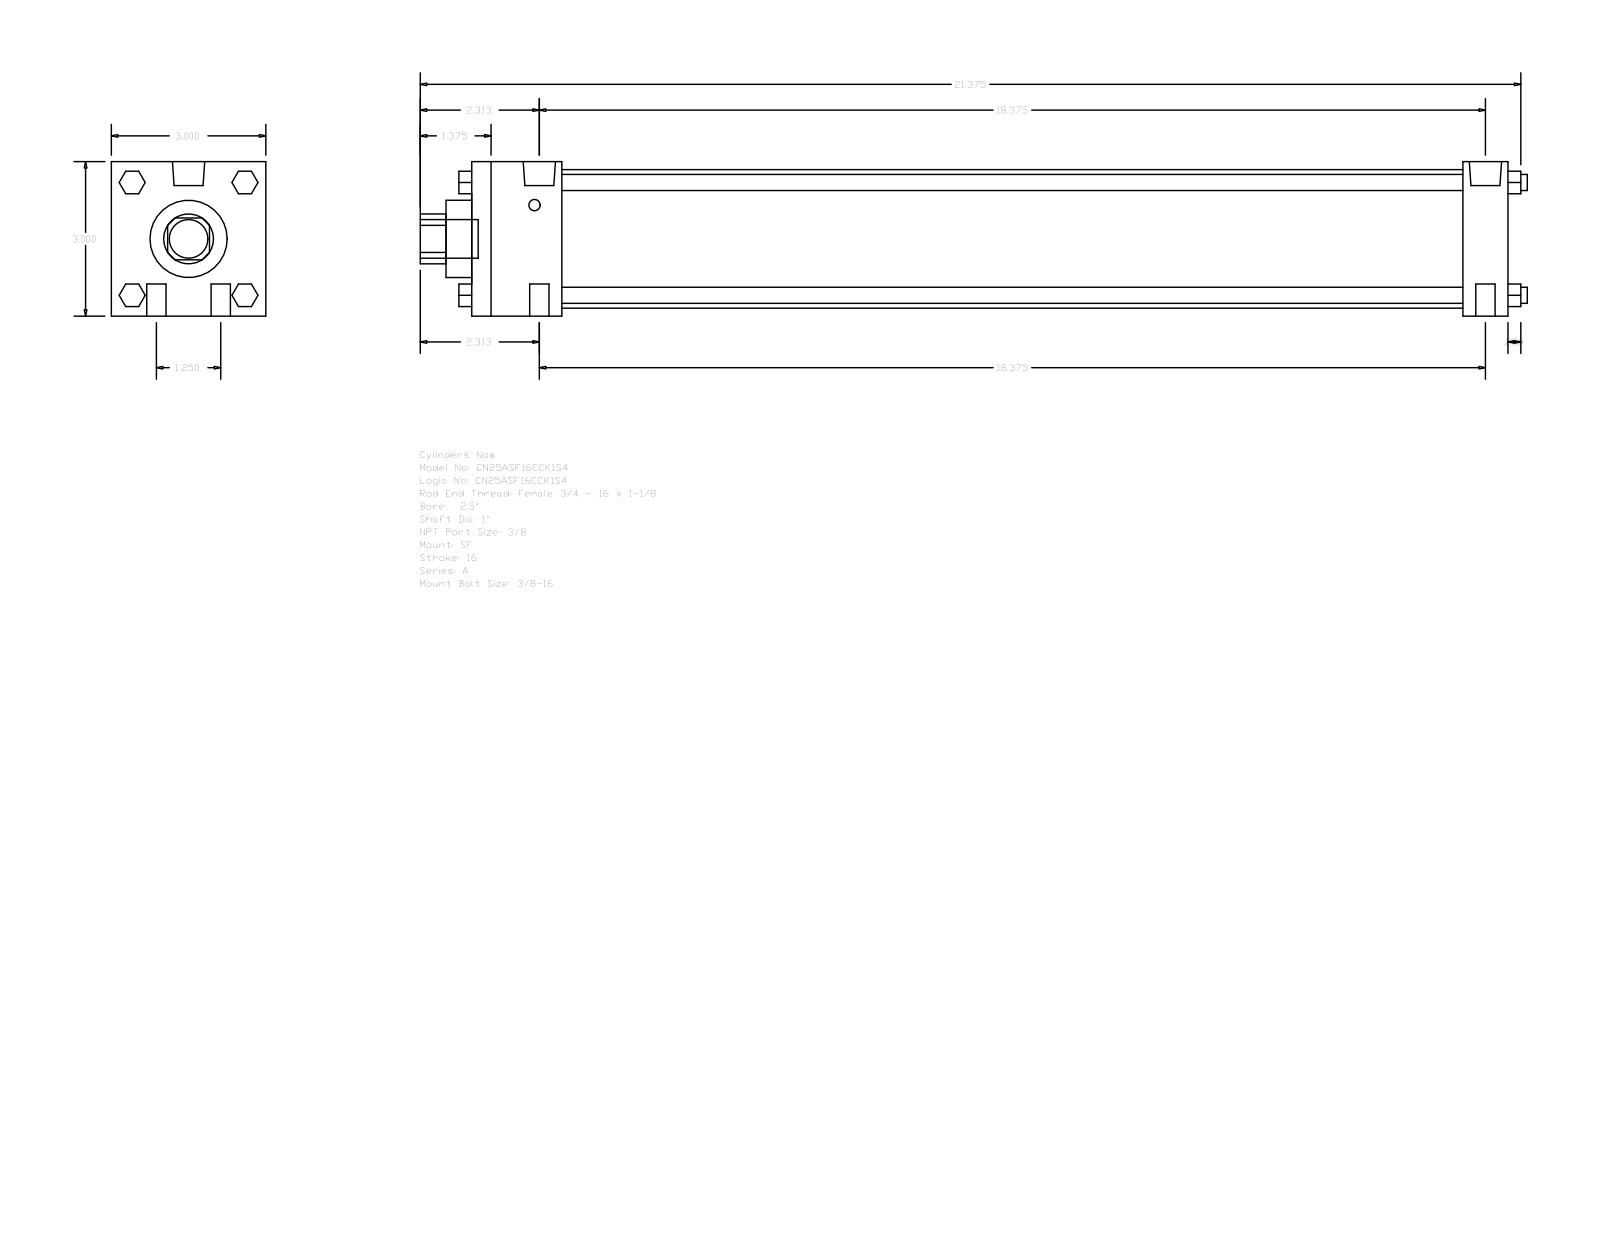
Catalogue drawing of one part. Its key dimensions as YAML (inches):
part_name: "A_SF__0250_1"
step_written_by: "GSSL Pune (CONFIG_CONTROL_DESIGN)"
units: inches
bodies: {solids: 0, faces: 124, planar: 94, cylindrical: 30, other: 0}
overall_size: [21.5, 3, 3]
round_holes:
  - {diameter: 1, count: 1}
  - {diameter: 1.5, count: 1}
  - {diameter: 2.69, count: 1}
round_bosses_or_shafts:
  - {diameter: 0.375, count: 4}
  - {diameter: 0.313, count: 4}
  - {diameter: 0.627, count: 2}
  - {diameter: 0.219, count: 2}
  - {diameter: 0.75, count: 1}
partial_cylinders:
  - {radius: 0.484, count: 1}
face_to_face_distances: [3, 20.125, 19.25, 0.875, 1.75, 17.5, 18.375, 0.5, 0.437, 2.25]
